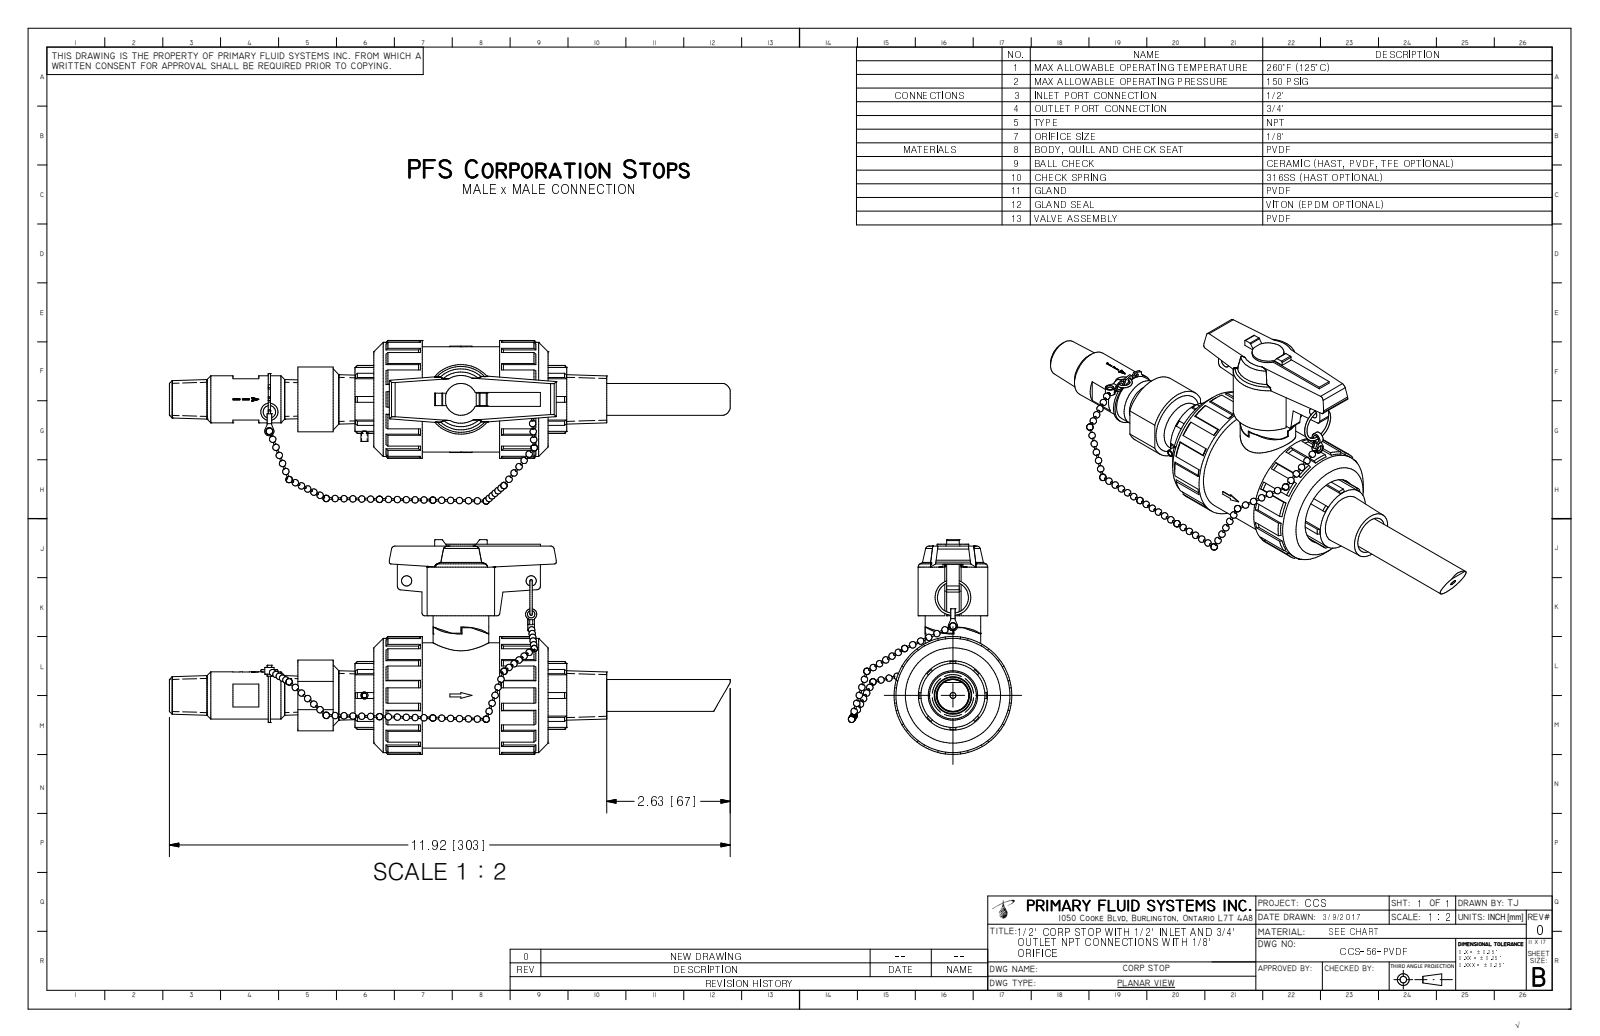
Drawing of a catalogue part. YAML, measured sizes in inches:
part_name: "CCS-56-PVDF_R0"
step_written_by: "Autodesk Inventor 2009 (AUTOMOTIVE_DESIGN)"
units: inches
bodies: {solids: 1, faces: 602, planar: 294, cylindrical: 78, other: 230}
overall_size: [11.922, 4.554, 3.473]
volume: 25.28
surface_area: 116.7
round_holes:
  - {diameter: 0.079, count: 1}
  - {diameter: 0.125, count: 1}
  - {diameter: 0.217, count: 1}
  - {diameter: 0.25, count: 1}
  - {diameter: 0.469, count: 1}
  - {diameter: 0.56, count: 1}
  - {diameter: 1.47, count: 1}
  - {diameter: 2.16, count: 1}
round_bosses_or_shafts:
  - {diameter: 2.5, count: 1}
  - {diameter: 2.422, count: 1}
  - {diameter: 2.232, count: 1}
  - {diameter: 1.801, count: 1}
  - {diameter: 1.476, count: 1}
  - {diameter: 1.36, count: 1}
  - {diameter: 1.181, count: 1}
  - {diameter: 1.18, count: 1}
partial_cylinders:
  - {radius: 0.02, count: 4}
  - {radius: 0.079, count: 4}
  - {radius: 0.039, count: 2}
  - {radius: 0.043, count: 2}
  - {radius: 0.059, count: 2}
  - {radius: 0.157, count: 2}
  - {radius: 0.337, count: 1}
  - {radius: 0.463, count: 1}
face_to_face_distances: [0.039, 0.266, 0.306, 0.472, 3.233, 0.23, 3.475, 0.242, 3.003, 1.03]
hole_center_spacings: [0.535]
